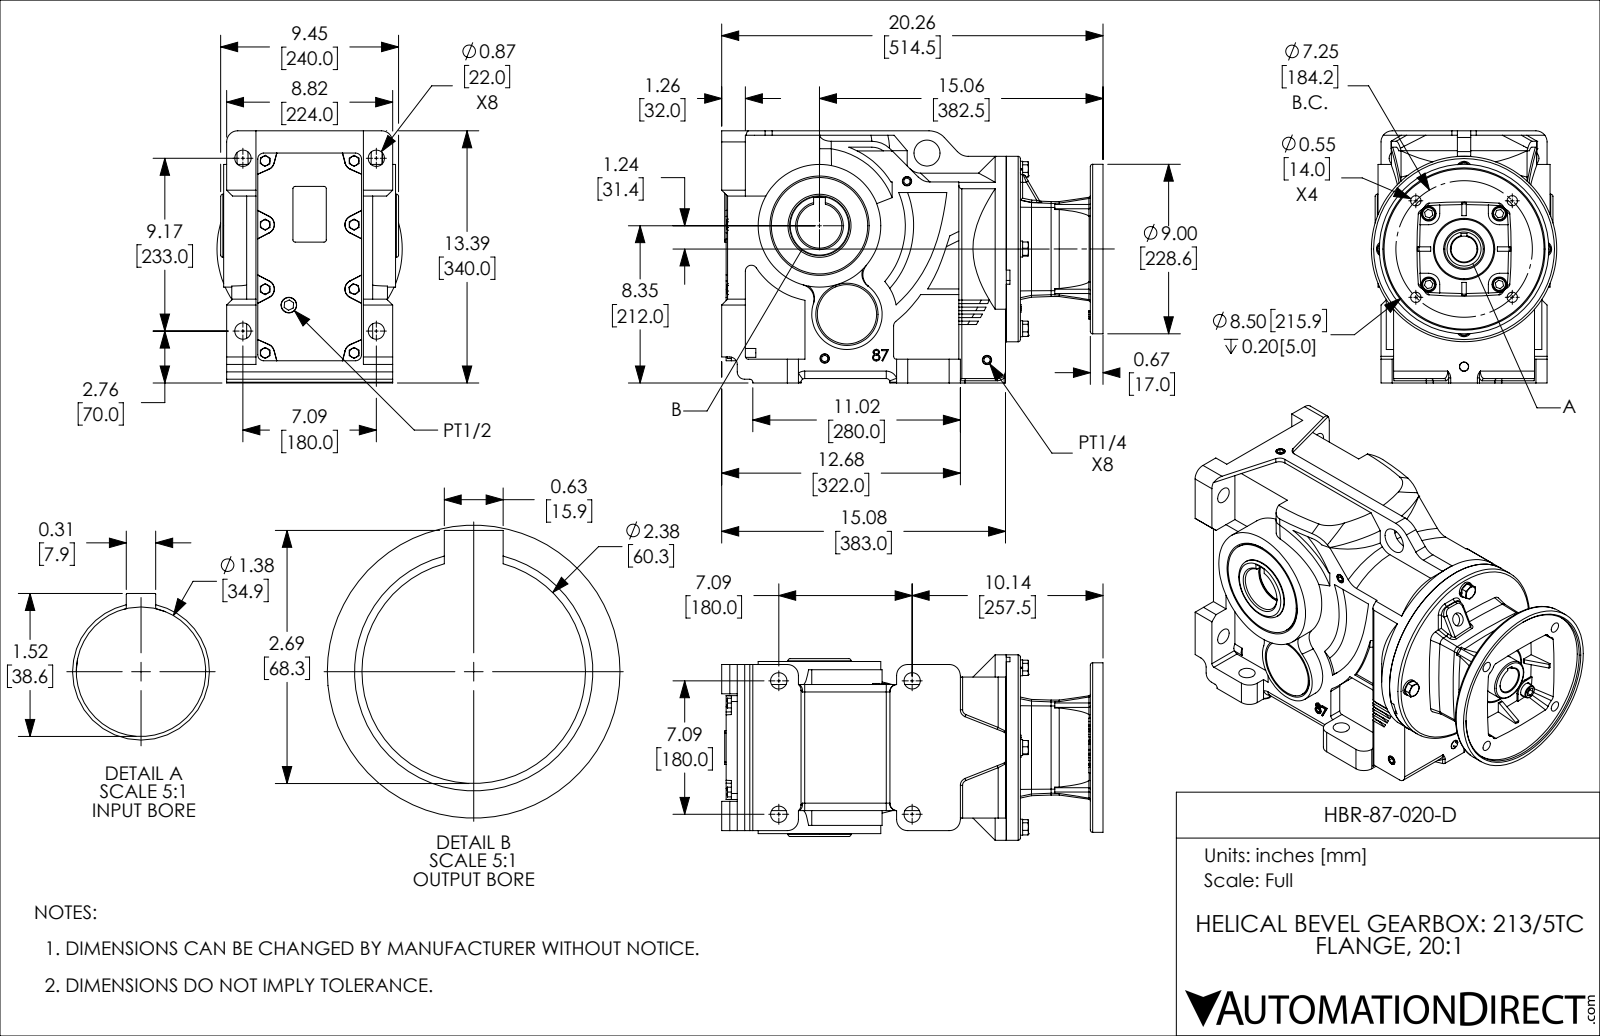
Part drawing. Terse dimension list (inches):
name: HBR-87-020-D
written by: SolidWorks 2018 (AUTOMOTIVE_DESIGN)
unit: in
bodies: 9 solids, 1185 faces (575 planar, 309 cylindrical, 301 other)
size: 20.256 × 13.501 × 9.843
volume: 1 441 in³; area: 1 528 in²
holes: 8× ⌀0.551, 8× ⌀0.866, 4× ⌀0.48, 4× ⌀0.496, 4× ⌀0.787, 1× ⌀0.473, 1× ⌀0.709, 1× ⌀0.827, 1× ⌀1.125, 1× ⌀1.376, 1× ⌀1.378, 1× ⌀1.417
bosses: 4× ⌀0.846, 4× ⌀0.709, 4× ⌀0.472, 2× ⌀3.15, 1× ⌀9.843, 1× ⌀9, 1× ⌀6.513, 1× ⌀5.118
rounds: 22× R0.591, 17× R0.394, 15× R0.118, 7× R0.157, 6× R0.315, 4× R0.008, 4× R0.236, 4× R0.472
face distances: 0.669, 0.236, 6.024, 1.063, 7.087, 13.15, 0.394, 14.882, 1.22, 1.89
hole spacings: 3.011, 6.394, 4.495, 7.087, 7.263, 2.657, 3.059, 3.758
